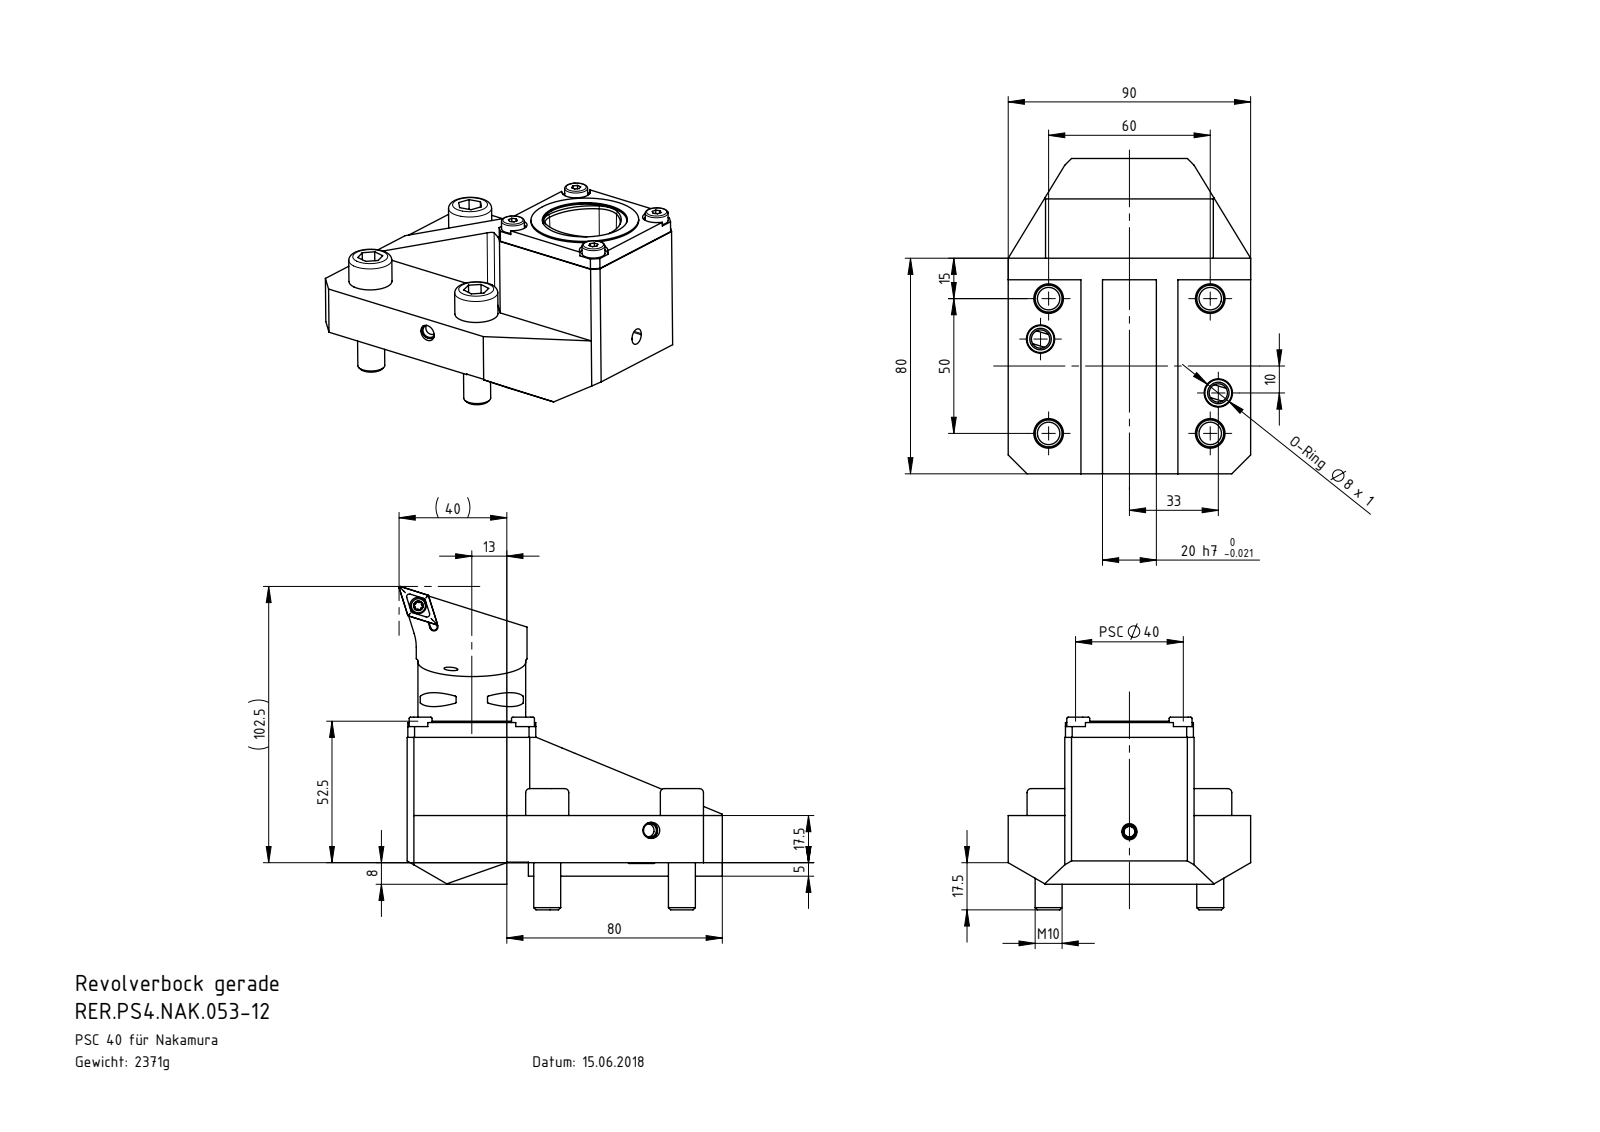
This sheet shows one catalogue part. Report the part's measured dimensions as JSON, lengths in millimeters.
{"part_name": "ISO 8752 3x10; RER.PS4.NAK.053-12; DIN 7984 - M5 x 16; DIN 3771 - 37x1.5 (+8 more)", "step_written_by": "SolidWorks 2017 (CONFIG_CONTROL_DESIGN)", "units": "millimeters", "bodies": {"solids": 26, "faces": 826, "planar": 328, "cylindrical": 198, "other": 300}, "overall_size": [117, 90, 71.5], "volume_mm3": 273723, "surface_area_mm2": 77685, "round_holes": [[4.2, 4], [5.5, 4], [11, 4], [2.5, 3], [3, 2], [3.3, 2], [5, 2], [6.8, 2], [10.5, 2], [2.1, 1], [4, 1], [6, 1]], "round_bosses_or_shafts": [[16, 4], [10, 4], [8.5, 4], [5, 4], [3, 3], [5.5, 2], [40, 1], [39.7, 1]], "partial_cylinders_radius": [[3.5, 4], [5.25, 4], [2.75, 2], [3, 2], [7, 2], [9, 1], [12, 1]], "face_to_face_distances": [17.5, 35, 21, 69, 22.5, 55, 14, 34, 25.5, 12.5], "hole_center_spacings": [20.25, 26.87, 36.36, 38, 50, 12, 12.69, 14.21]}
